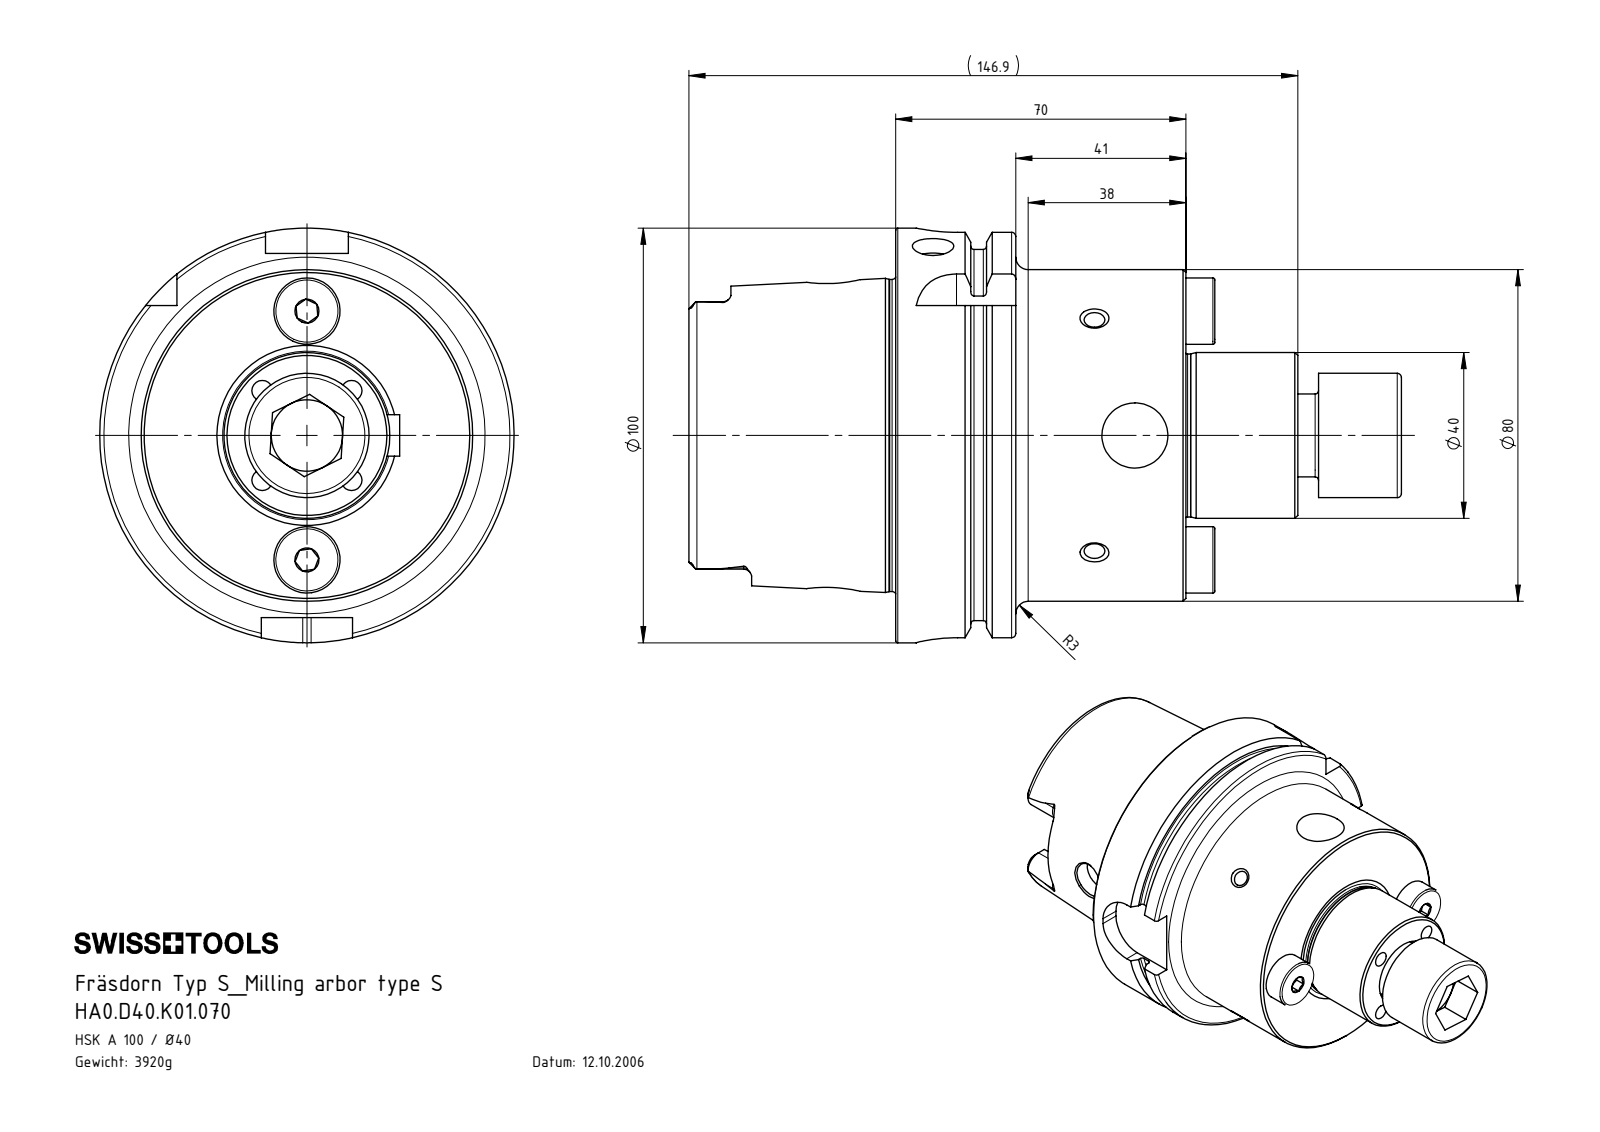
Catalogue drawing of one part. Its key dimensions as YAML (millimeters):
part_name: "HA0.D40.K01.070; D40-ER2.001.023_B; D40-ER1.002.040_A_Default; HA0-D40.K01.070_C_Fertigbearbeitung"
step_written_by: "SolidWorks 2011 (AUTOMOTIVE_DESIGN)"
units: millimeters
bodies: {solids: 4, faces: 359, planar: 84, cylindrical: 112, other: 163}
overall_size: [171.9, 100, 100]
volume: 500284
surface_area: 79019
round_holes:
  - {diameter: 5, count: 9}
  - {diameter: 10, count: 3}
  - {diameter: 12, count: 2}
  - {diameter: 14, count: 2}
  - {diameter: 17.5, count: 1}
  - {diameter: 21, count: 1}
  - {diameter: 22.5, count: 1}
  - {diameter: 26, count: 1}
  - {diameter: 53, count: 1}
  - {diameter: 63, count: 1}
round_bosses_or_shafts:
  - {diameter: 16, count: 2}
  - {diameter: 6, count: 2}
  - {diameter: 4.6, count: 2}
  - {diameter: 100, count: 1}
  - {diameter: 91.95, count: 1}
  - {diameter: 80, count: 1}
  - {diameter: 75.26, count: 1}
  - {diameter: 40, count: 1}
partial_cylinders:
  - {radius: 1.9, count: 6}
  - {radius: 4.88, count: 4}
  - {radius: 10, count: 4}
  - {radius: 5, count: 2}
face_to_face_distances: [70, 28.95, 41.05, 12.45, 16.5, 57.55, 49.9, 62.35, 78.85, 119.9]
hole_center_spacings: [11.05, 15.25, 22.04, 30, 42.18, 30.49, 60]
